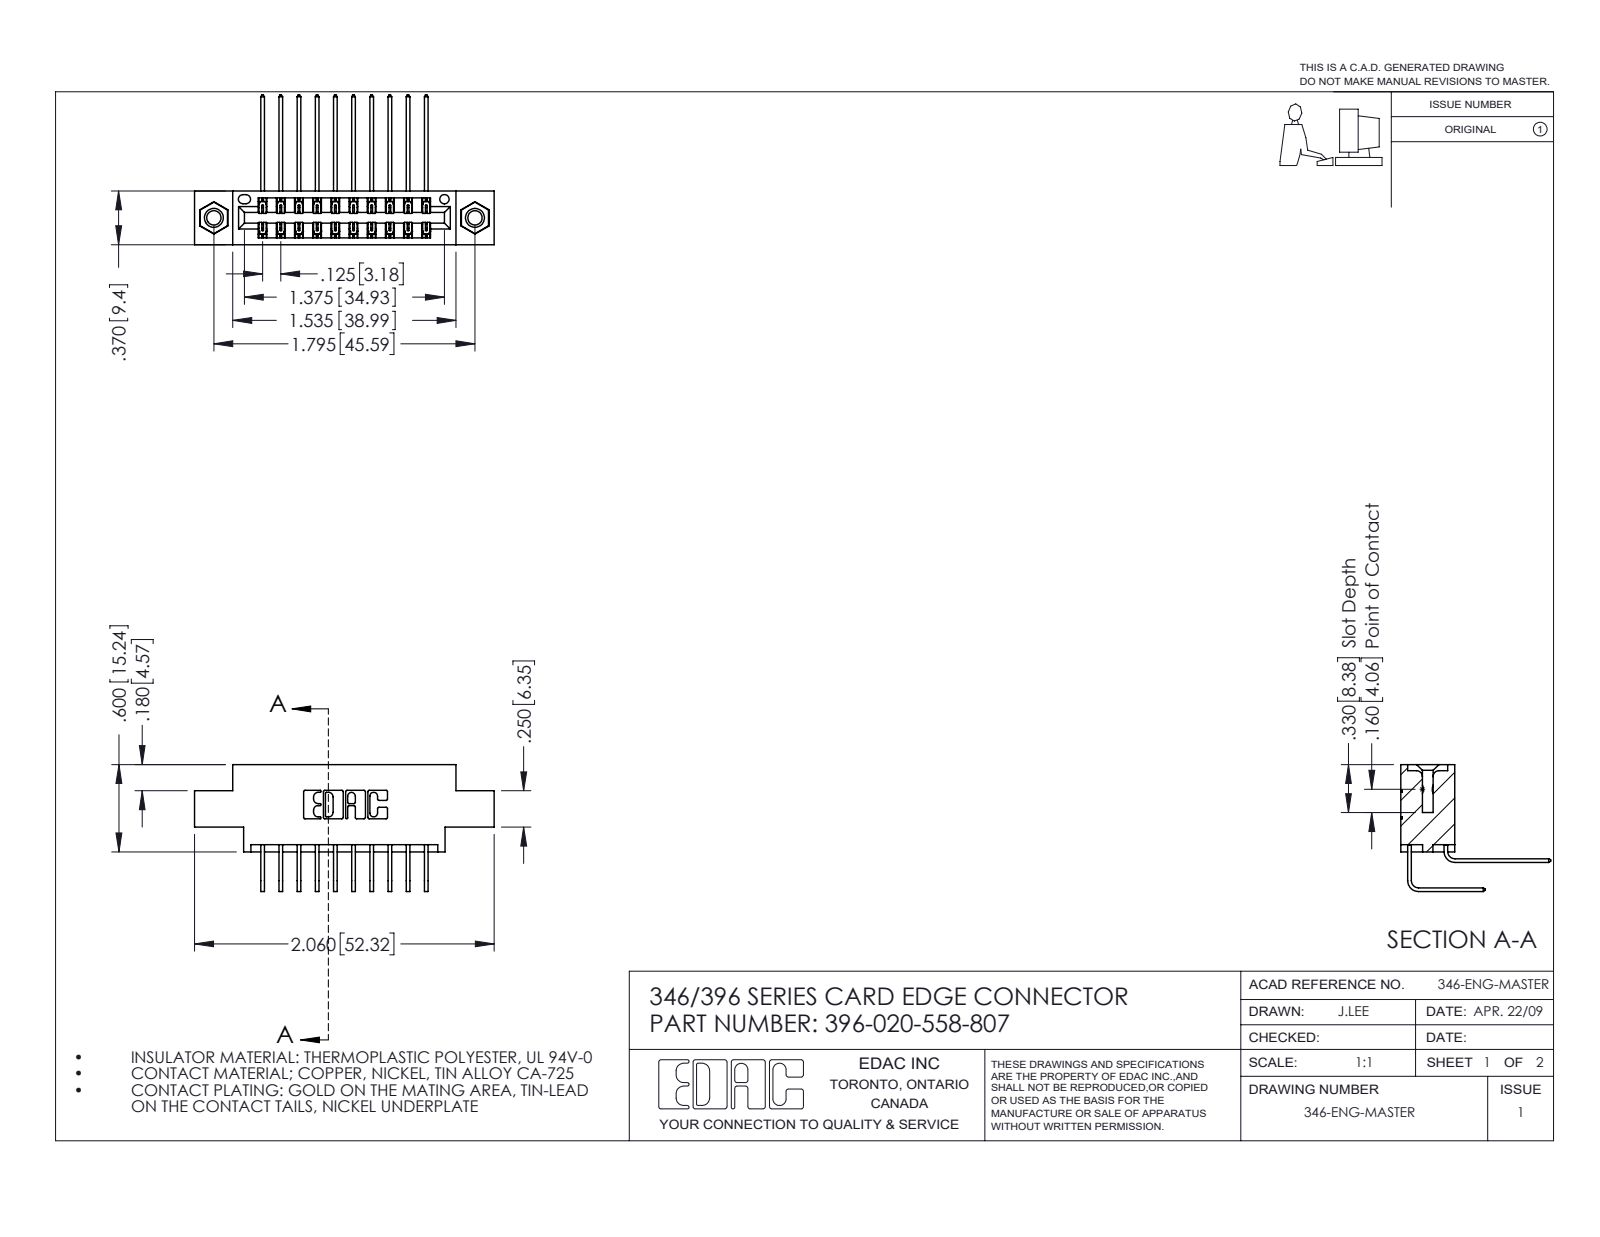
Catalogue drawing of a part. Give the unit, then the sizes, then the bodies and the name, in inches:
Units: inches
Overall size (bounding box): 2.06 × 1.03 × 0.873
Round holes (diameter × count): ⌀0.098 ×2, ⌀0.125 ×2, ⌀0.156 ×2, ⌀0.064 ×1
Round bosses / shafts (diameter × count): ⌀0.155 ×2
Partial cylindrical surfaces — rounded edges, fillets, slot ends (radius × count): R0.006 ×30, R0.01 ×22, R0.007 ×6, R0.031 ×6, R0.026 ×3, R0.014 ×2, R0.022 ×2, R0.024 ×2
Main face-to-face distances: 0.25, 0.048, 0.322, 0.37, 0.025, 0.072, 0.298, 0.222, 0.148, 0.275
Hole centre spacings: 0.246, 1.59, 1.795
Volume: 0.293 in³ · Surface area: 10.64 in²
Bodies: 23 solids, 1266 faces (852 planar, 398 cylindrical, 16 other)
Part name (STEP PRODUCT): 345-292-001_558 Tail - 2; 346 Part_0.170 Offset - 0.156 Dia-TI; 345-292-001_558 559 Tail - 1; 396-020-558-807 (+1 more)
STEP written by: SolidWorks 2016 (CONFIG_CONTROL_DESIGN)
